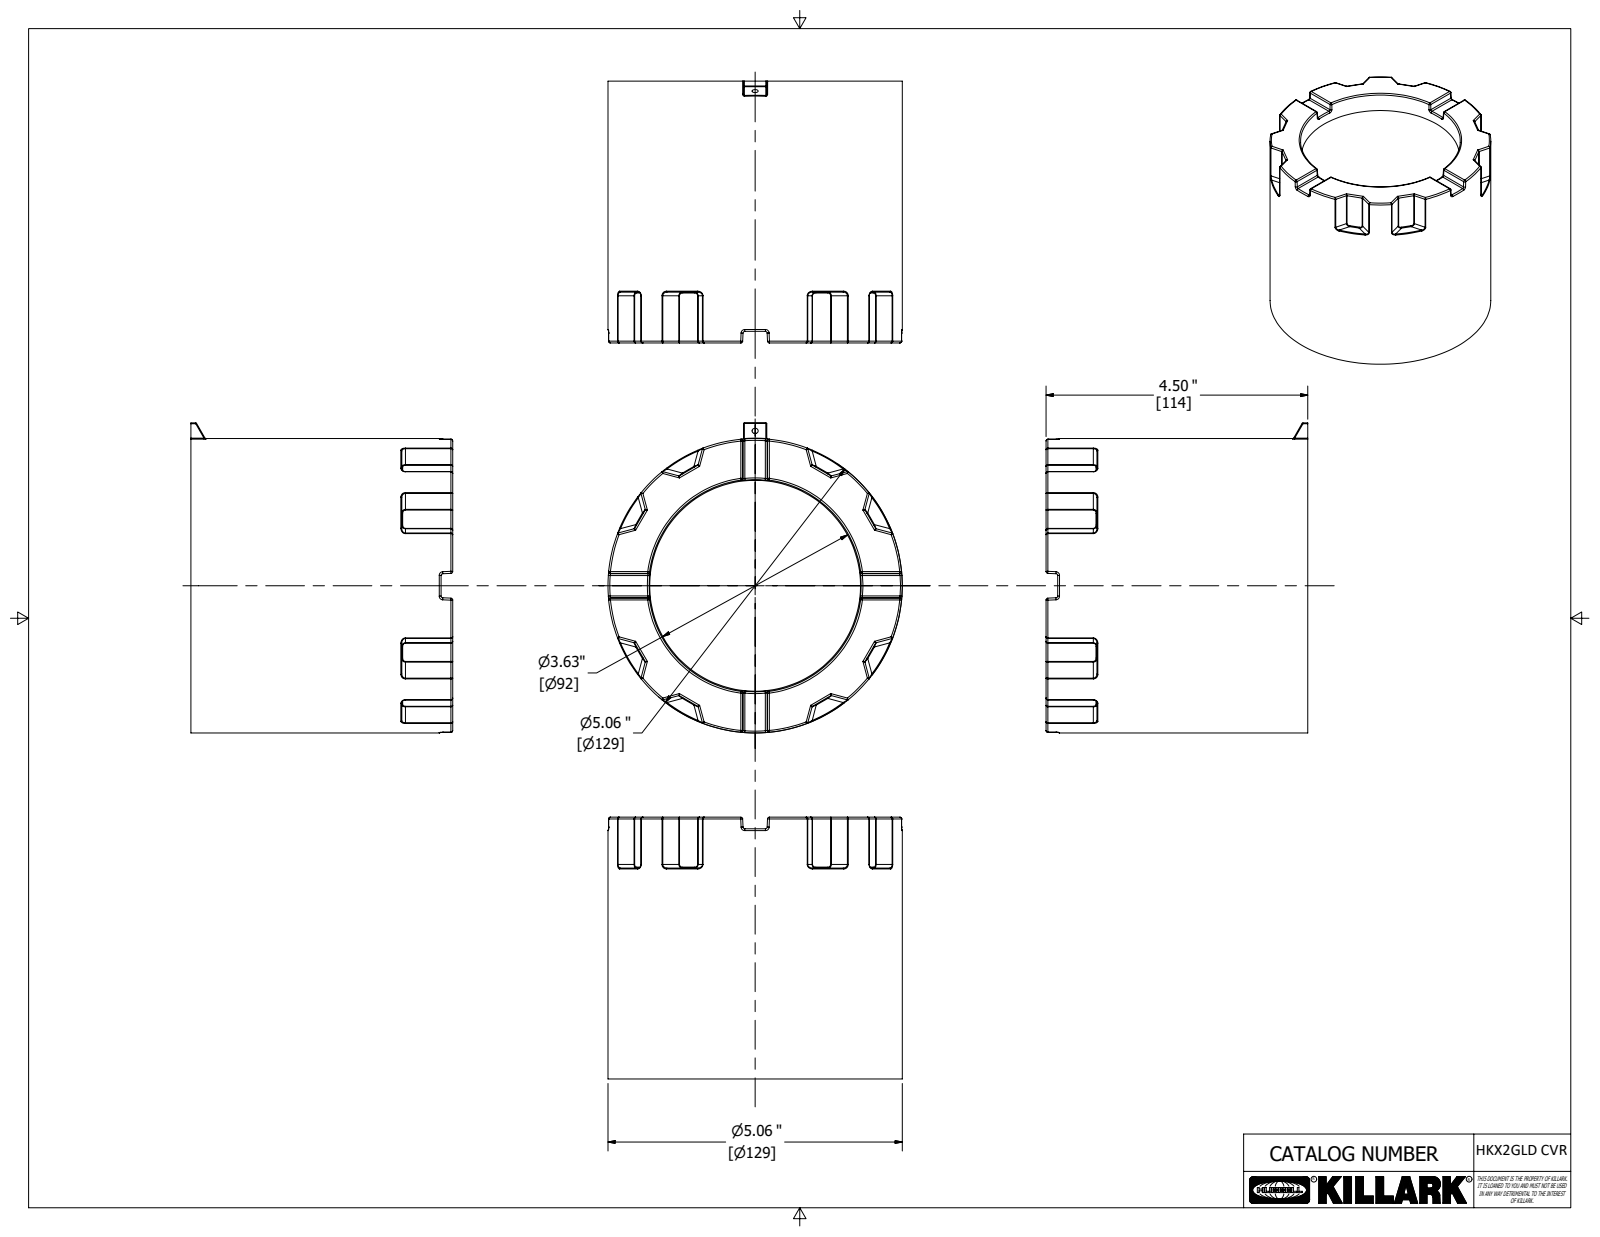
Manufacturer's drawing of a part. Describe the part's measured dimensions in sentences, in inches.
The part is named "51640ABAM for web". Its 3-D file was written by "Autodesk Inventor 2020 (AUTOMOTIVE_DESIGN)". It is 1 solid with 319 faces: 54 planar, 108 cylindrical and 157 other. Overall it measures 5.33 by 5.06 by 4.5 inches. Its volume is 28.64 cubic inches and its surface area 146.7 square inches. Round holes: 1 of diameter 0.104, 1 of diameter 4.1, 1 of diameter 4.39, 1 of diameter 4.86. Round bosses or shafts: 1 of diameter 5.06. Partial cylindrical surfaces (rounded edges, fillets, slot ends): 47 of radius 0.016, 32 of radius 0.031, 16 of radius 0.062. The main face-to-face distances are 4.5, 2.969, 4.05, 0.45, 4.574, 4.3, 0.25, 0.2, 2.97, 2.97.
